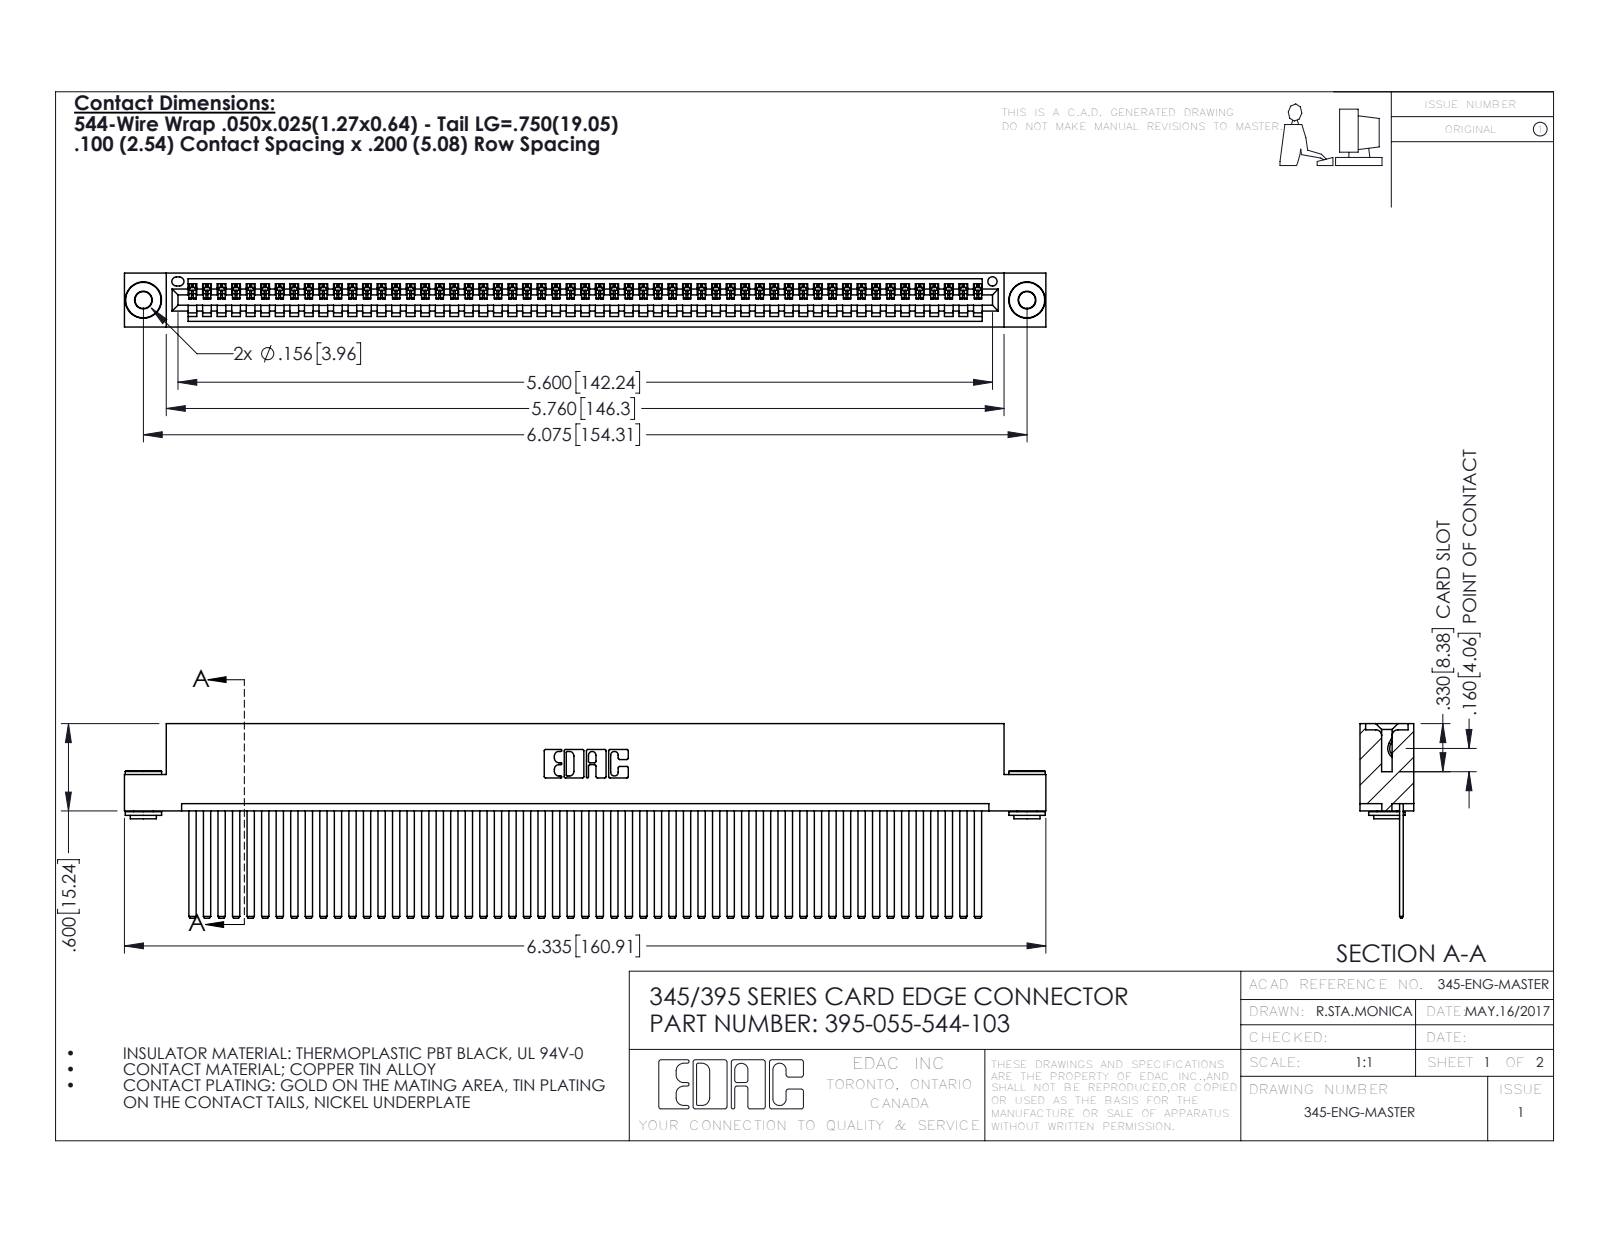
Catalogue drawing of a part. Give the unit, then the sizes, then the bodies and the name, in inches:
Units: inches
Overall size (bounding box): 6.335 × 1.337 × 0.37
Round holes (diameter × count): ⌀0.116 ×2, ⌀0.156 ×2, ⌀0.064 ×1
Round bosses / shafts (diameter × count): ⌀0.25 ×2, ⌀0.18 ×2, ⌀0.136 ×2
Partial cylindrical surfaces — rounded edges, fillets, slot ends (radius × count): R0.006 ×110, R0.01 ×22, R0.007 ×6, R0.031 ×6, R0.026 ×3, R0.031 ×2, R0.04 ×2, R0.014 ×1
Main face-to-face distances: 0.072, 0.298, 0.025, 0.098, 0.272, 0.37, 0.2, 0.225, 0.149, 0.072
Hole centre spacings: 0.27, 5.839, 6.075
Volume: 0.979 in³ · Surface area: 36.62 in²
Bodies: 58 solids, 3024 faces (2070 planar, 946 cylindrical, 8 other)
Part name (STEP PRODUCT): 395-055-544-103; 345-292-001_345-293-144; 345-250-002_345-250-002-102; 345 Part_Flush Mounting Lugs - 0.156 Dia-TH
STEP written by: SolidWorks 2016 (CONFIG_CONTROL_DESIGN)
